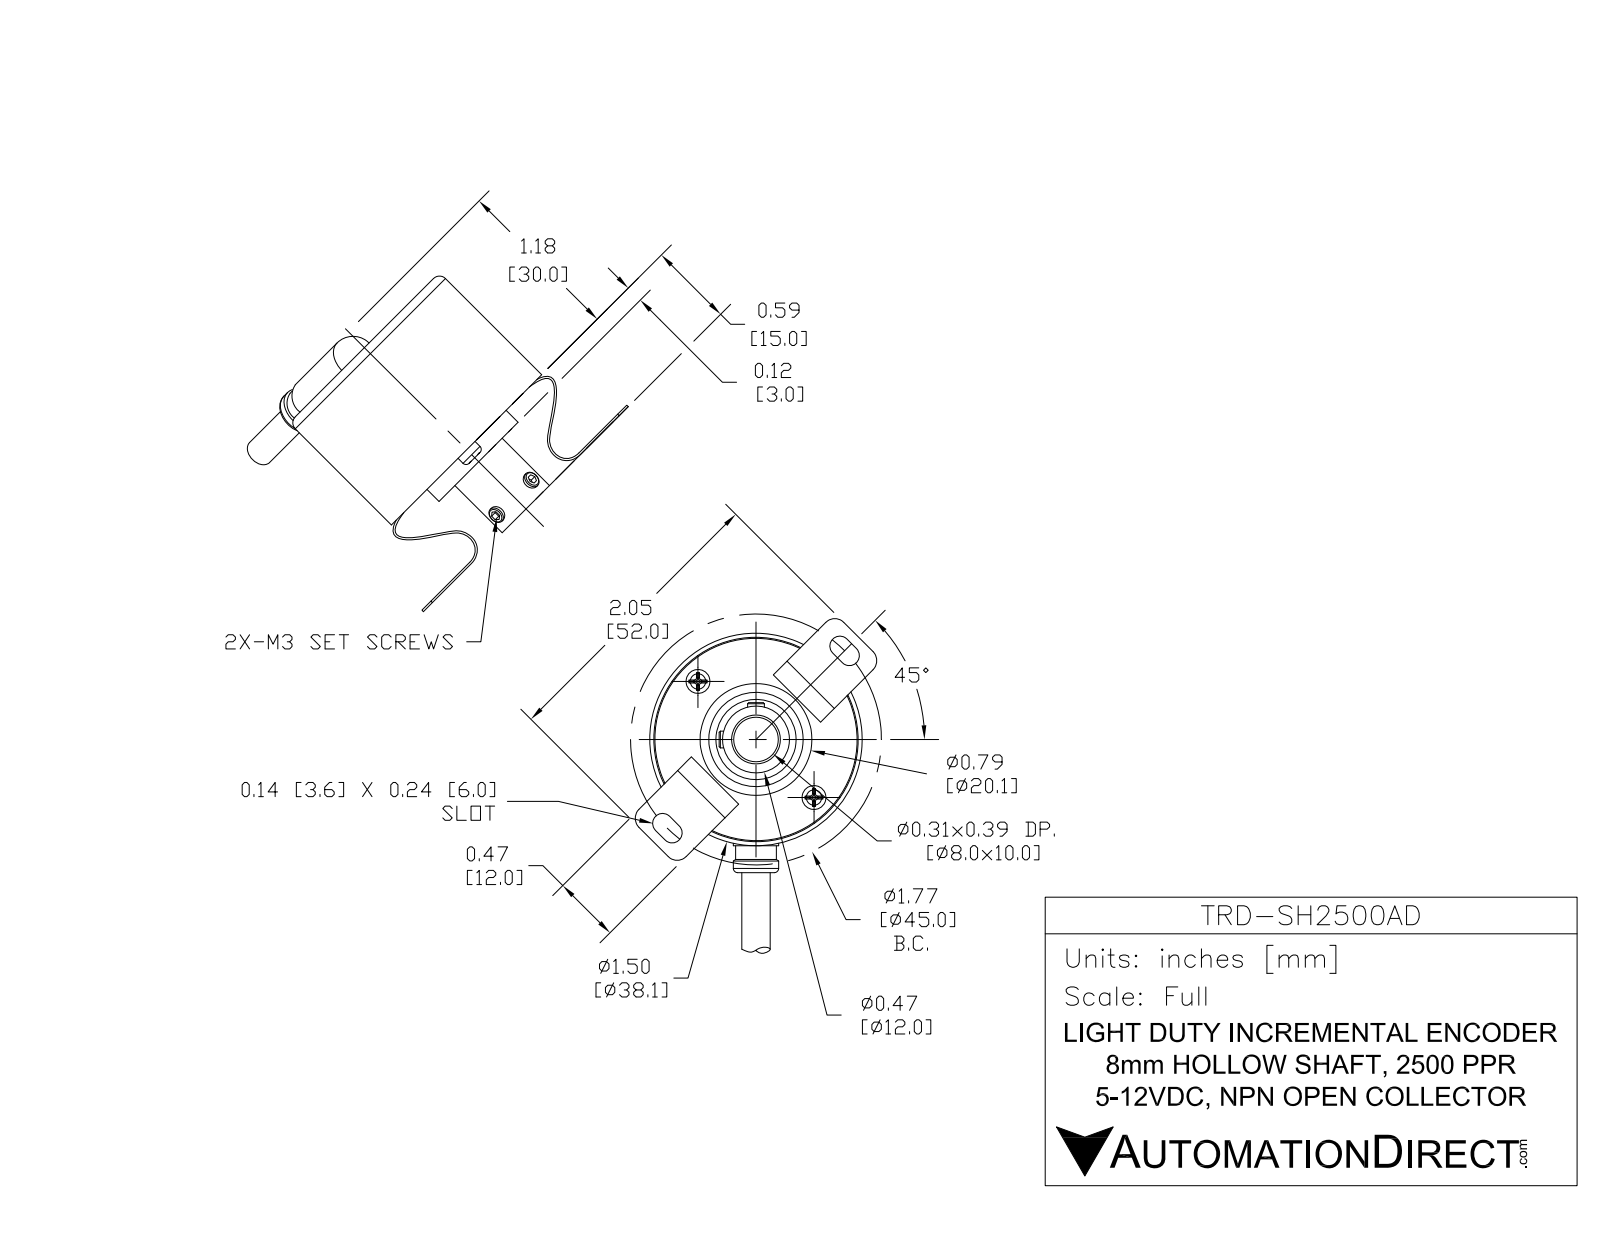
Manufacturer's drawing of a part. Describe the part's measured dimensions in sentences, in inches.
The part is named "TRD-SH2500AD". Its 3-D file was written by "SolidWorks 2016 (AUTOMOTIVE_DESIGN)". It is 11 solids with 322 faces: 169 planar, 101 cylindrical and 52 other. Overall it measures 3.952 by 1.772 by 1.684 inches. Its volume is 2.043 cubic inches and its surface area 17.32 square inches. Round holes: 5 of diameter 0.126, 2 of diameter 0.098, 1 of diameter 0.315, 1 of diameter 0.791. Round bosses or shafts: 5 of diameter 0.118, 1 of diameter 1.496, 1 of diameter 0.787, 1 of diameter 0.591, 1 of diameter 0.472, 1 of diameter 0.299, 1 of diameter 0.197, 1 of diameter 0.134. Partial cylindrical surfaces (rounded edges, fillets, slot ends): 6 of radius 0.039, 5 of radius 0.118, 4 of radius 0.03, 4 of radius 0.071, 4 of radius 0.087, 4 of radius 0.098, 2 of radius 0.031, 2 of radius 0.146. The main face-to-face distances are 1.024, 0.579, 1.035, 0.591, 1.614, 1.602, 0.567, 0.118, 1.142, 0.106. The hole center spacings are 0.551, 0.78, 0.955, 0.285, 0.285, 0.954, 1.065, 1.065.
